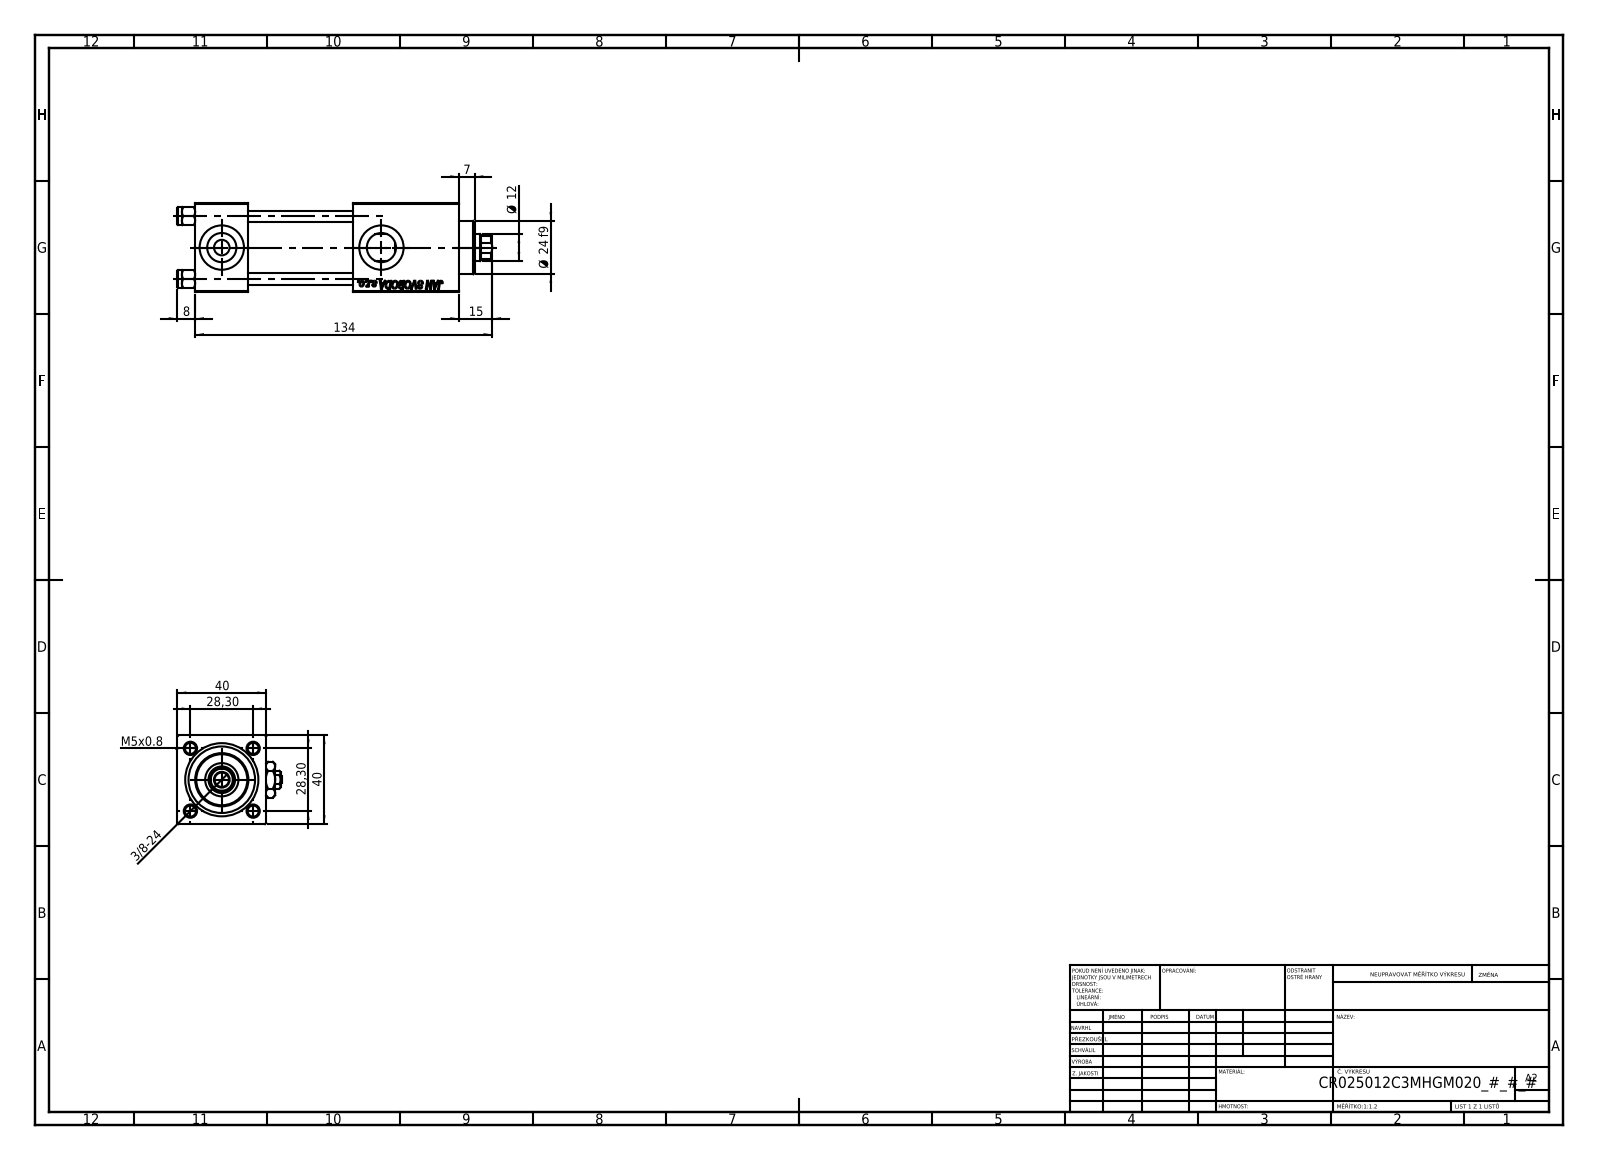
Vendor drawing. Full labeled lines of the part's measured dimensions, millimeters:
Part name (STEP PRODUCT): V215_VC_A; V215CR_C_Body; Zatka_pro_OIL_PORT; V215CR_C_TYCINKA (+2 more)
STEP written by: SolidWorks 2019 (CONFIG_CONTROL_DESIGN)
Units: millimetres
Bodies: 13 solids, 1248 faces (572 planar, 98 cylindrical, 578 other)
Overall size (bounding box): 142 × 47 × 40
Volume: 140 985 mm³ · Surface area: 56 209 mm²
Round holes (diameter × count): ⌀5 ×4, ⌀20 ×3, ⌀7 ×2, ⌀13.16 ×2, ⌀6.5 ×1, ⌀12 ×1, ⌀15 ×1, ⌀25 ×1, ⌀30 ×1
Round bosses / shafts (diameter × count): ⌀8 ×4, ⌀31 ×1, ⌀24 ×1
Partial cylindrical surfaces — rounded edges, fillets, slot ends (radius × count): R5.5 ×1
Main face-to-face distances: 40, 24, 39.8, 90.3, 66.3, 48, 47, 71, 19.3, 119
Hole centre spacings: 20.01, 28.3, 40.02, 72
